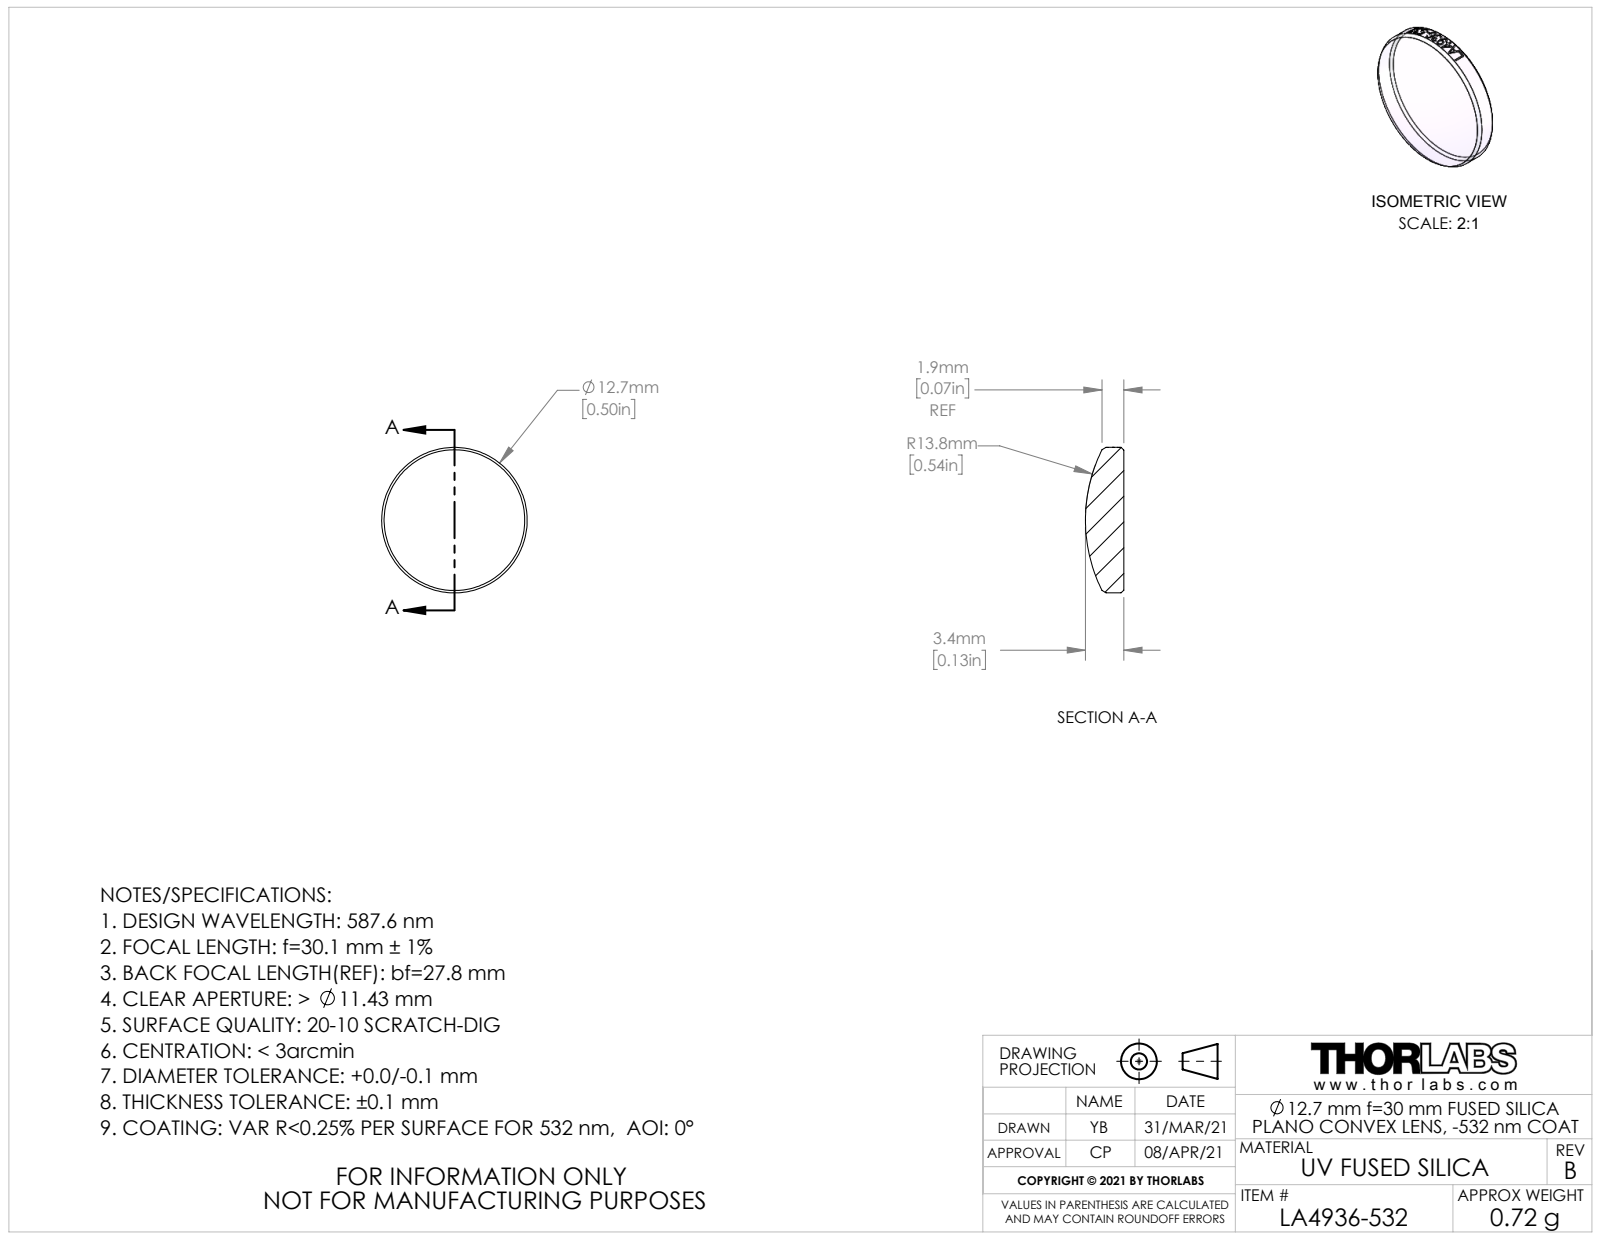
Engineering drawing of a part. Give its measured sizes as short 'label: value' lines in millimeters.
name: CTN015719-E0W
written by: SolidWorks 2018 (AUTOMOTIVE_DESIGN)
unit: mm
bodies: 1 solid, 23 faces (1 planar, 16 cylindrical, 6 other)
size: 12.7 × 12.7 × 3.34
volume: 325 mm³; area: 324 mm²
bosses: 1× ⌀12.7
